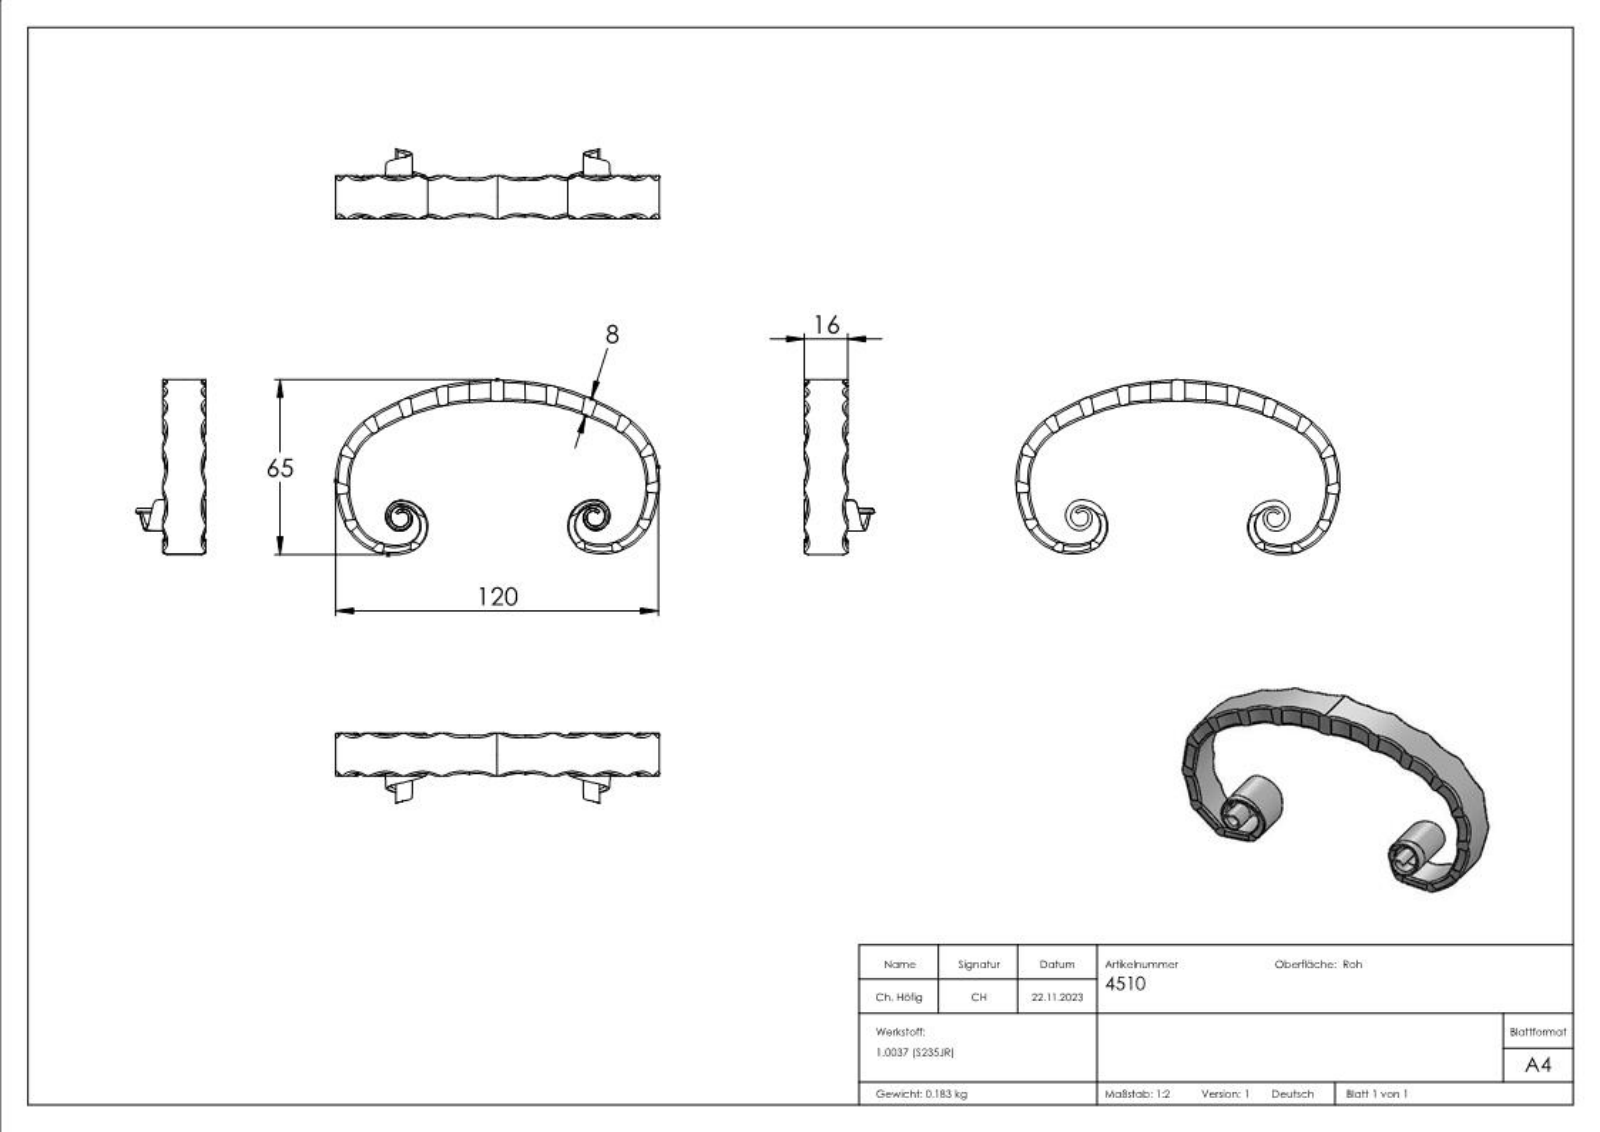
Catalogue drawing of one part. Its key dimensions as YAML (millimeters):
part_name: "4510"
step_written_by: "SolidWorks 2018 (CONFIG_CONTROL_DESIGN)"
units: millimeters
bodies: {solids: 1, faces: 196, planar: 60, cylindrical: 40, other: 96}
overall_size: [120.19, 65, 26.71]
volume: 23437
surface_area: 13713
partial_cylinders:
  - {radius: 13, count: 40}
face_to_face_distances: [16]
